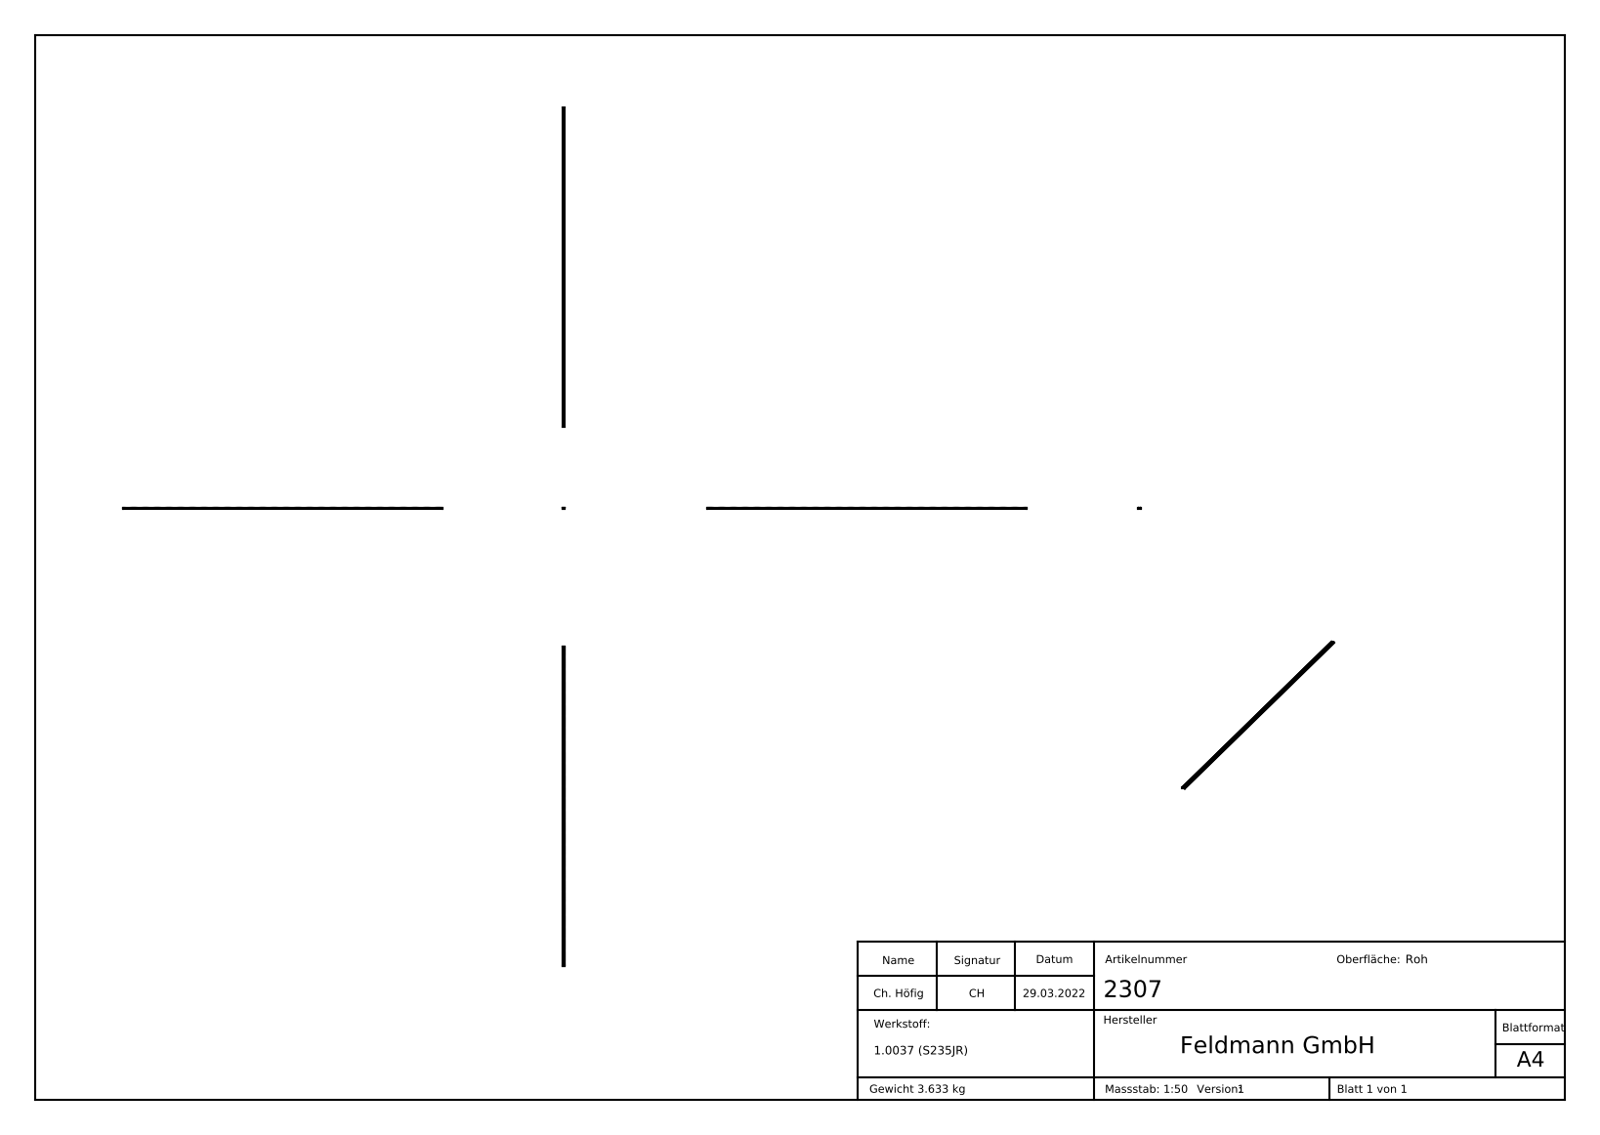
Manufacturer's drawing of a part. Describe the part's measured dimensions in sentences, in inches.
The part is named "2307". Its 3-D file was written by "SolidWorks 2018 (CONFIG_CONTROL_DESIGN)". It is 1 solid with 1413 faces: 1314 planar, 2 cylindrical and 97 other. Overall it measures 118.11 by 0.984 by 0.315 inches. Its volume is 28.42 cubic inches and its surface area 307.8 square inches. Partial cylindrical surfaces (rounded edges, fillets, slot ends): 2 of radius 0.139. The main face-to-face distances are 0.197, 0.984, 0.584, 0.438, 0.146, 1.022, 0.73, 1.315, 1.461, 1.899.
